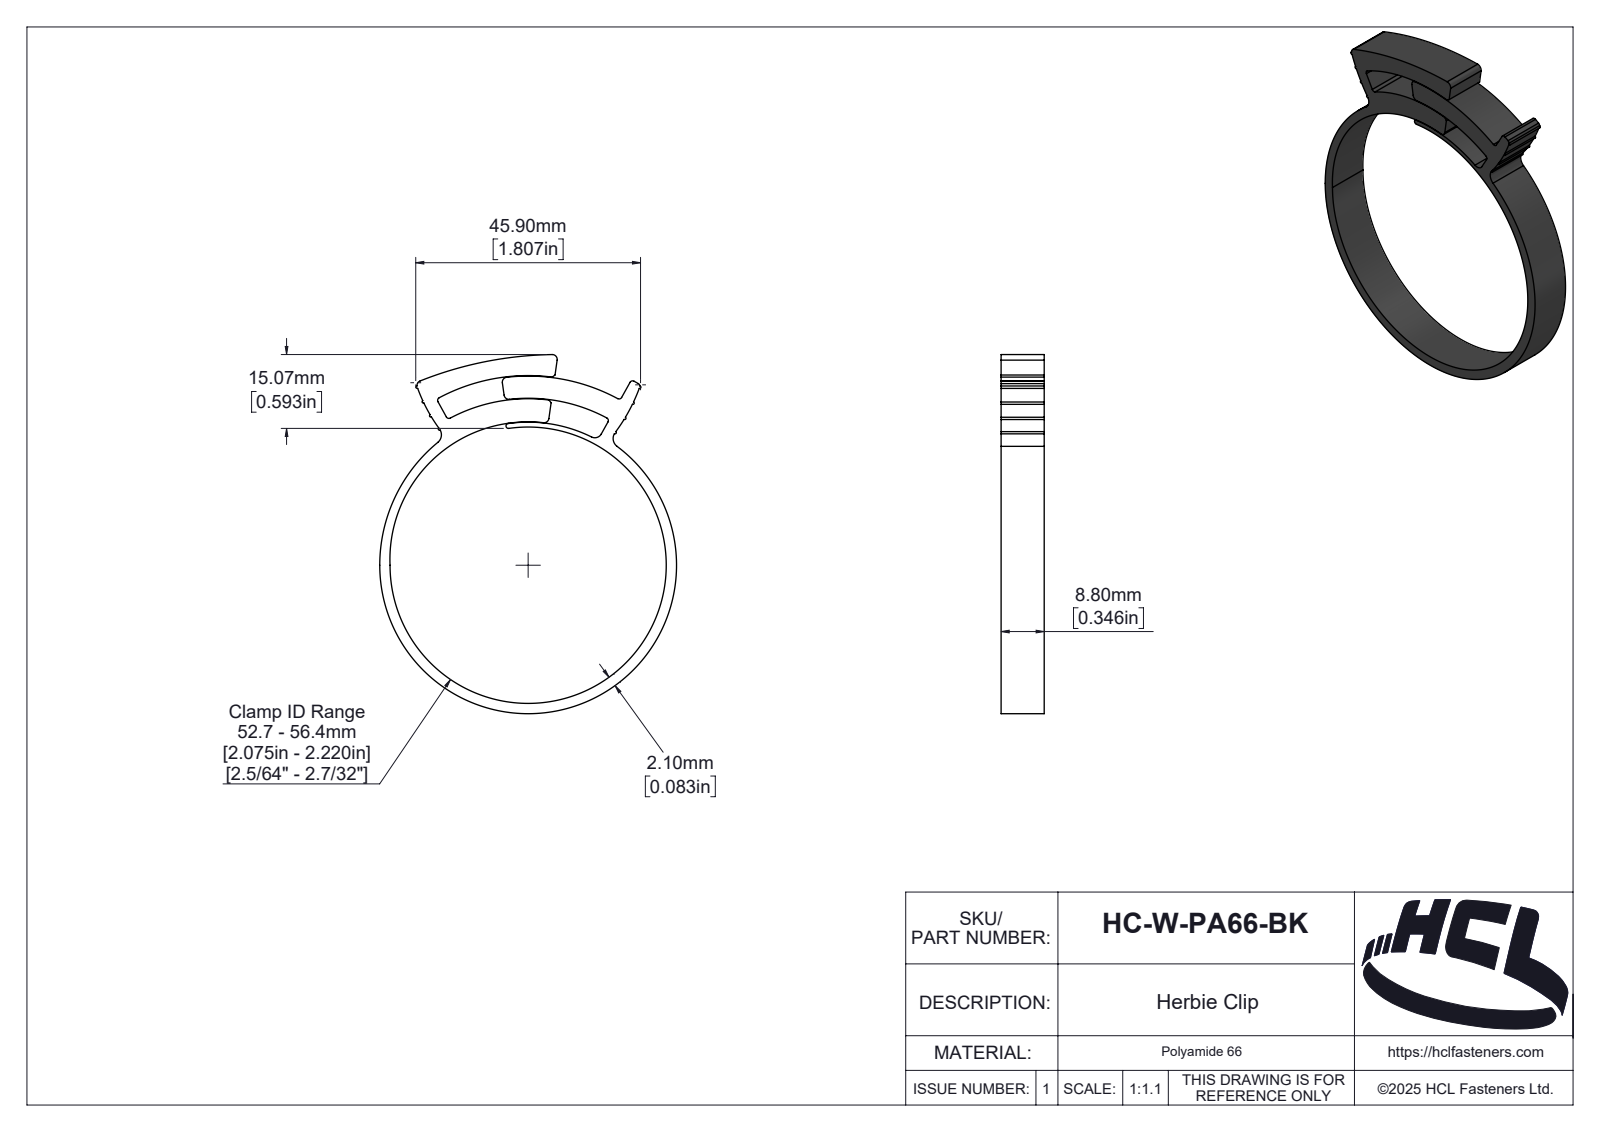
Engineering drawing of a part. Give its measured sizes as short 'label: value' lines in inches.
name: HC-W-PA66-BK
written by: SolidWorks 2025 (AUTOMOTIVE_DESIGN)
unit: in
bodies: 1 solid, 162 faces (13 planar, 100 cylindrical, 49 other)
size: 2.885 × 2.386 × 0.346
volume: 0.383 in³; area: 9.56 in²
rounds: 8× R0.01, 6× R0.024, 5× R0.039, 2× R0.079, 1× R0.007, 1× R0.02, 1× R0.026, 1× R0.033
face distances: 0.346
